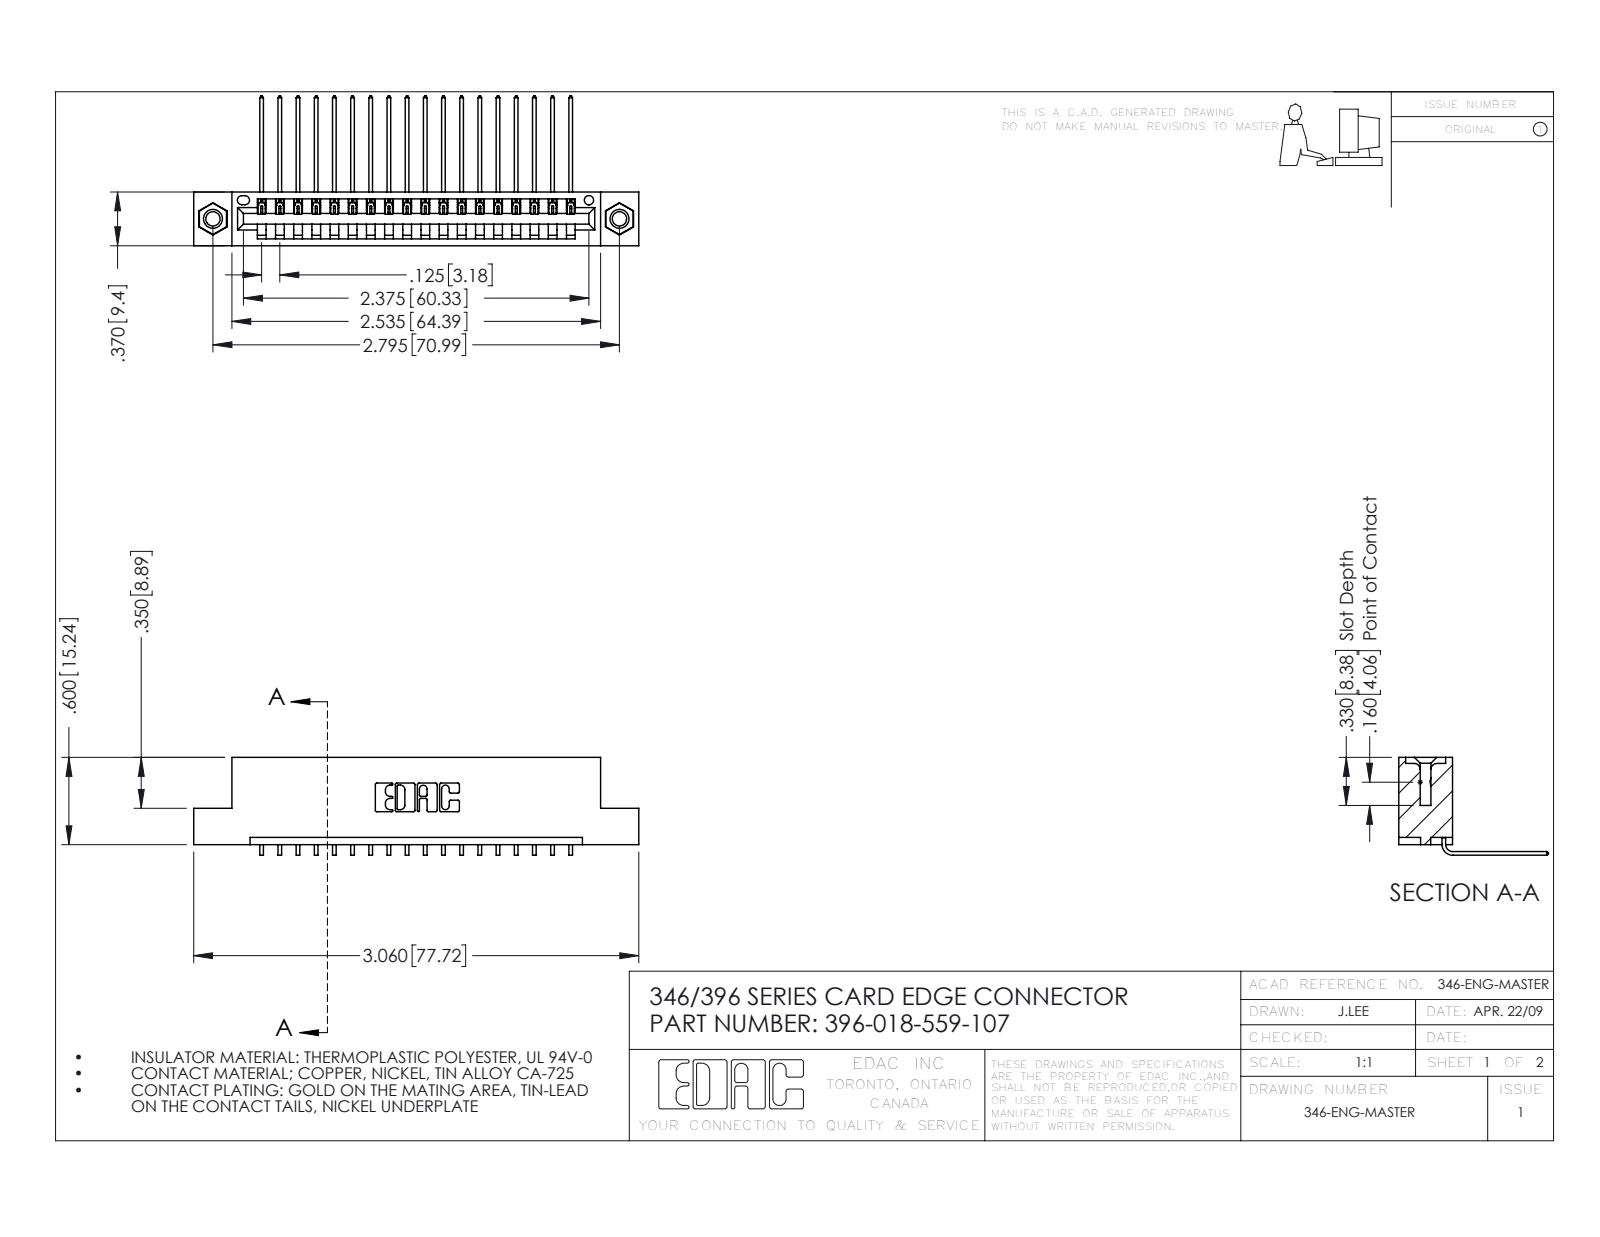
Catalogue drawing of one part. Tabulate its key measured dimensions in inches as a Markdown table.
| quantity | value |
| --- | --- |
| part name | 345-292-001_558 559 Tail - 1; 396-018-559-107; 345-250-001_345-250-005-103; 346 Part_Flush Mounting Lugs - 0.156 Dia-TI |
| STEP written by | SolidWorks 2016 (CONFIG_CONTROL_DESIGN) |
| units | inches |
| bodies | 21 solids, 1262 faces (864 planar, 382 cylindrical, 16 other) |
| overall size | 3.06 × 1.03 × 0.673 |
| volume | 0.447 in³ |
| surface area | 14.39 in² |
| round holes (diameter × count) | 0.098 × 2, 0.125 × 2, 0.156 × 2, 0.064 × 1 |
| round bosses / shafts (diameter × count) | 0.155 × 2 |
| partial cylindrical surfaces (radius × count) | 0.006 × 36, 0.01 × 22, 0.007 × 6, 0.031 × 6, 0.026 × 3, 0.031 × 2, 0.04 × 2, 0.014 × 1 |
| main face-to-face distances | 0.048, 0.322, 0.37, 0.25, 0.072, 0.025, 0.298, 0.148, 0.222, 0.1 |
| hole center spacings | 0.246, 2.588, 2.795 |
